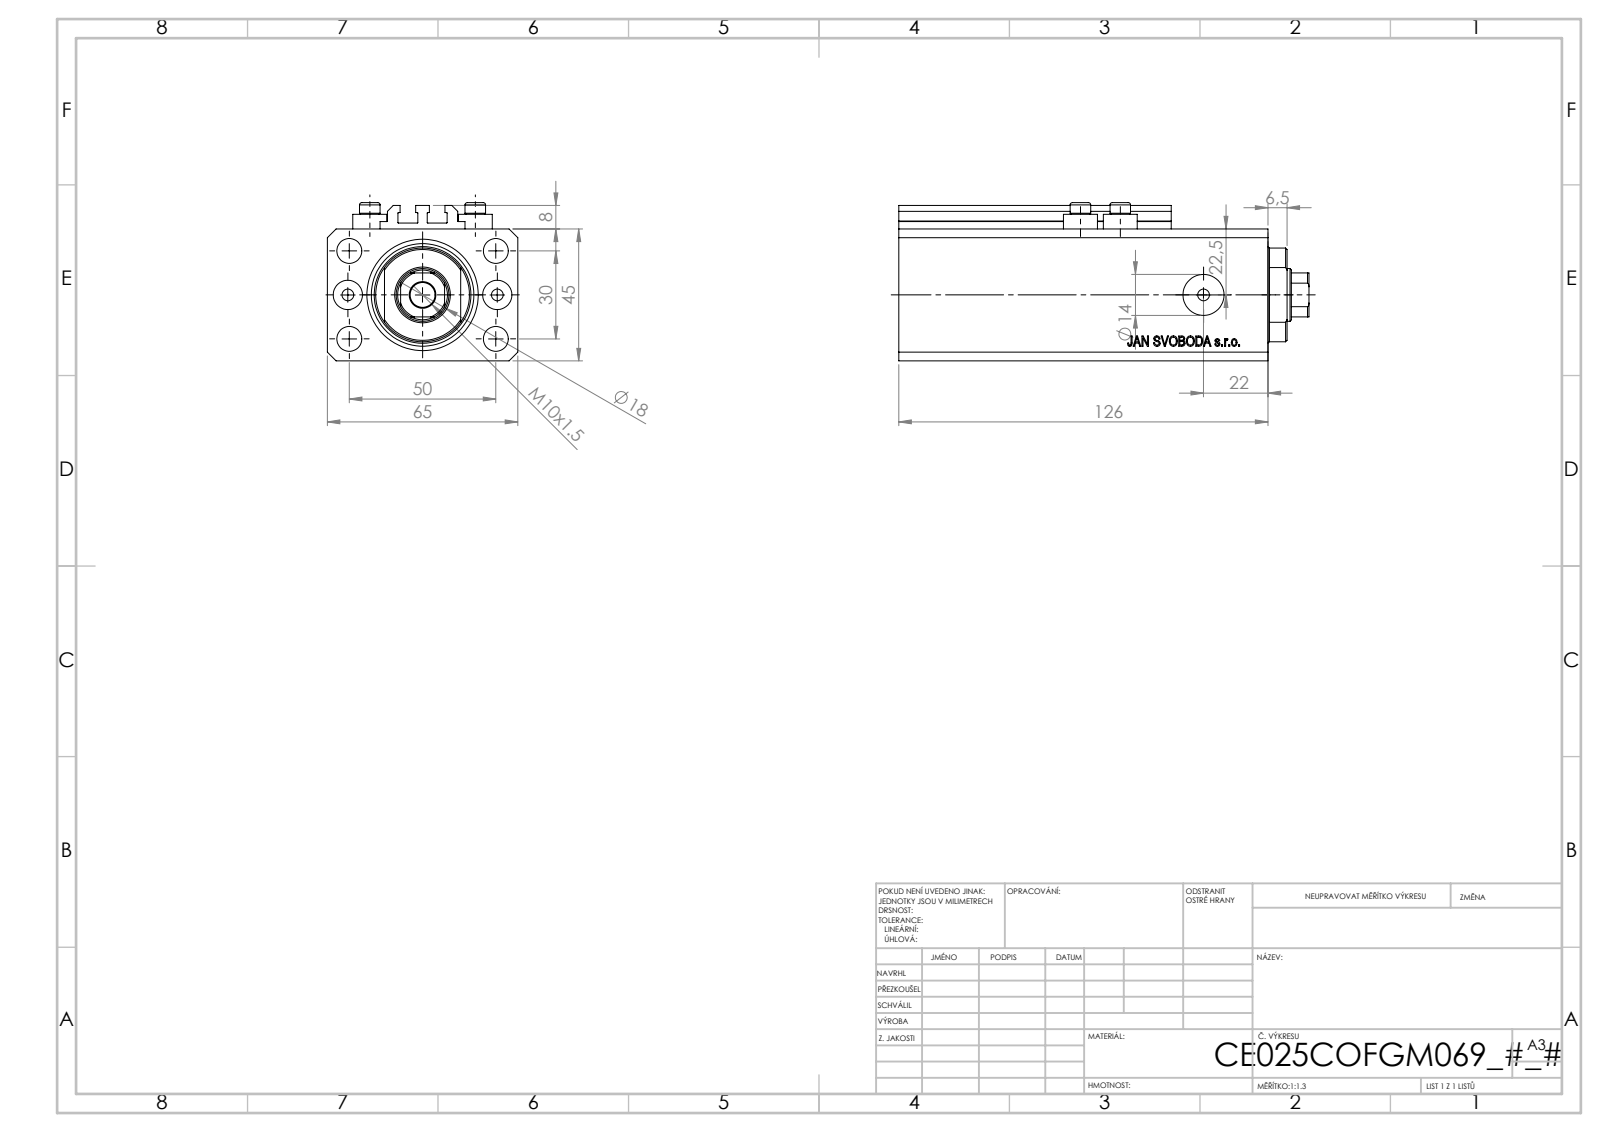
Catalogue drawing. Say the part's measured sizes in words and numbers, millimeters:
The part is named "V250CE_C_VCP; ALLEN BOLT V250CE; V250CE_C_Body; V250CE_VC_C". Its 3-D file was written by "SolidWorks 2019 (CONFIG_CONTROL_DESIGN)". It is 8 solids with 1034 faces: 504 planar, 86 cylindrical and 444 other. Overall it measures 140 by 65 by 54 millimeters. Its volume is 337 859 cubic millimeters and its surface area 84 493 square millimeters. Round holes: 8 of diameter 4, 5 of diameter 8.5, 2 of diameter 10, 2 of diameter 14, 1 of diameter 18, 1 of diameter 25, 1 of diameter 38. Round bosses or shafts: 4 of diameter 11.6, 4 of diameter 7. Partial cylindrical surfaces (rounded edges, fillets, slot ends): 10 of radius 0.2, 1 of radius 8.5, 1 of radius 16. The main face-to-face distances are 45, 65, 14, 47, 112, 126, 2.5, 2, 10, 20.5. The hole center spacings are 15.01, 29.15, 52.68, 13.6, 25.5, 30, 36, 38.48.
